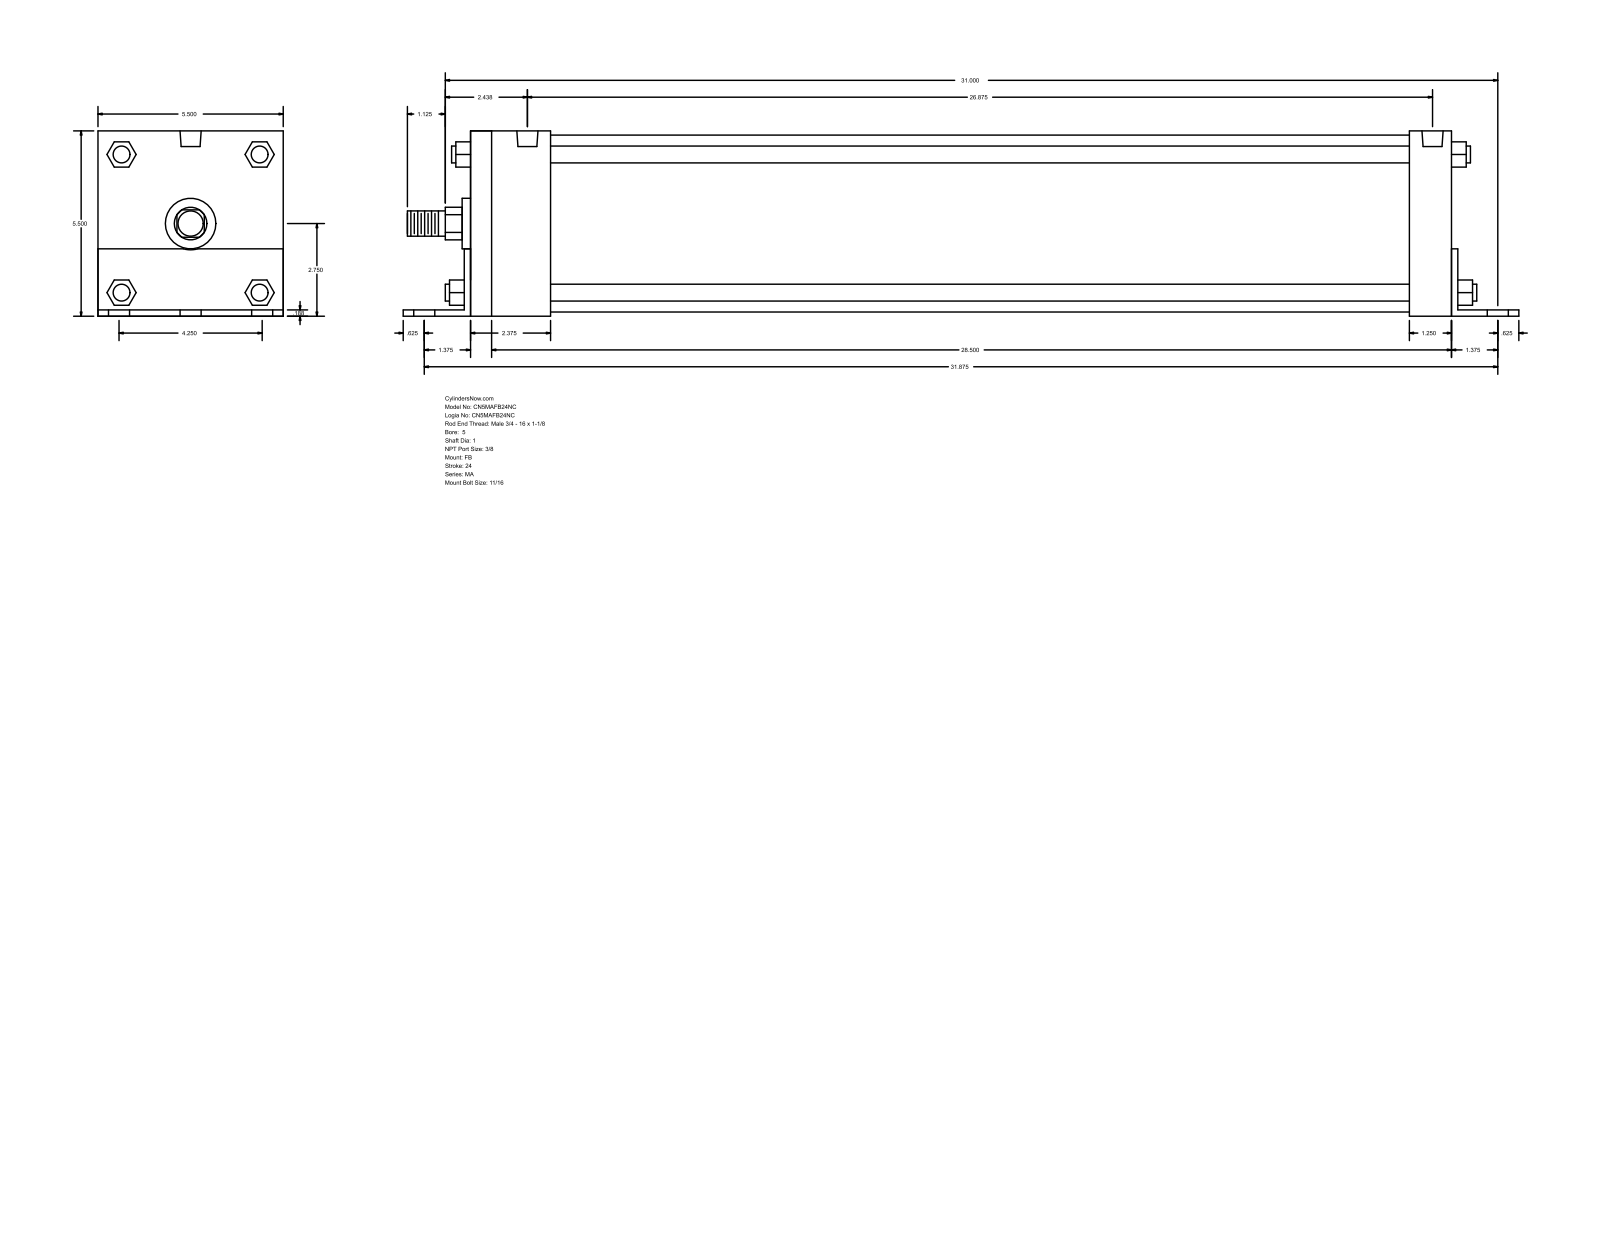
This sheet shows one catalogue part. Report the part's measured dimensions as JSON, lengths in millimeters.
{"part_name": "MA_FB__0500_1", "step_written_by": "GSSL Pune (CONFIG_CONTROL_DESIGN)", "units": "millimeters", "bodies": {"solids": 0, "faces": 140, "planar": 105, "cylindrical": 35, "other": 0}, "overall_size": [841.38, 139.75, 139.7], "round_holes": [[17.46, 6], [11.11, 4], [15.93, 2]], "round_bosses_or_shafts": [[12.7, 4], [133.35, 1], [38.1, 1], [25.4, 1], [19.05, 1]], "partial_cylinders_radius": [[12.29, 1], [19.81, 1]], "face_to_face_distances": [139.7, 4.76, 139.75, 744.54, 4.71, 134.99, 739.78, 749.3, 36.51, 31.75], "hole_center_spacings": [53.98, 811.43, 809.63, 73.04, 76.34, 94.68, 98.63, 107.96]}
